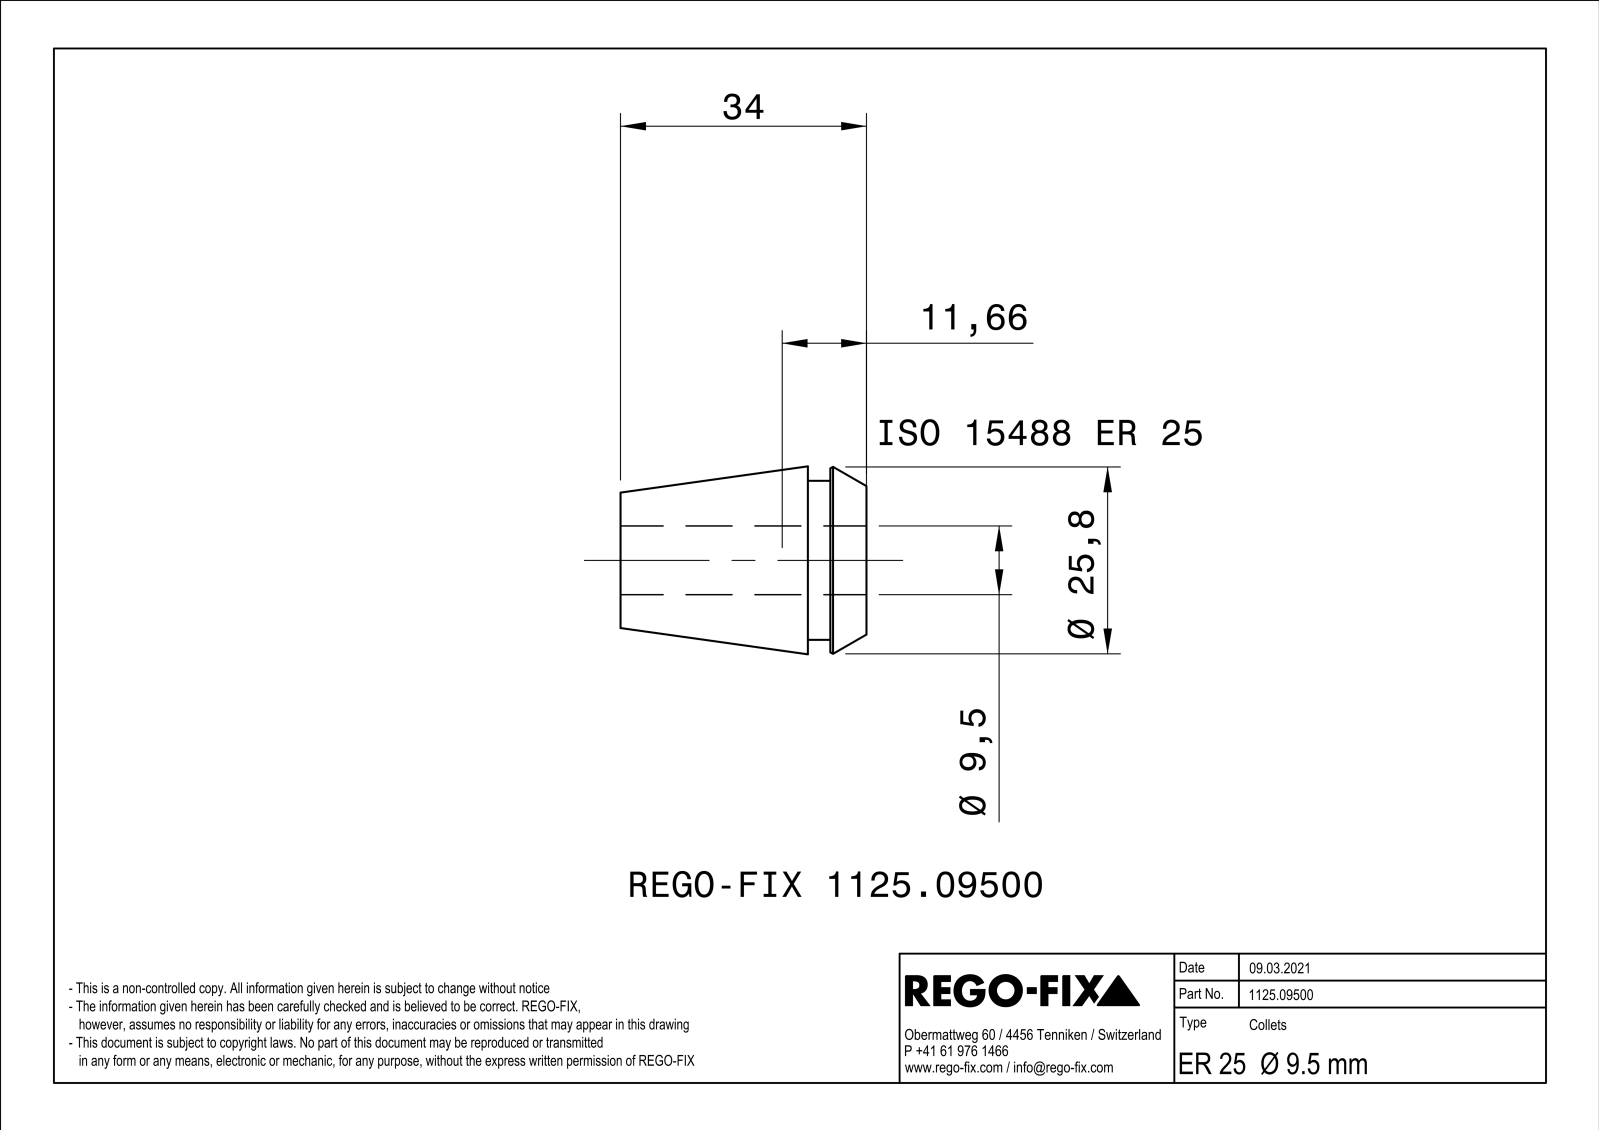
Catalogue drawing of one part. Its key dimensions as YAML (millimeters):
part_name: "NOCUT"
step_written_by: "SIEMENS PLM Software Solid Edge ST10 (AUTOMOTIVE_DESIGN)"
units: millimeters
bodies: {solids: 1, faces: 177, planar: 72, cylindrical: 25, other: 80}
overall_size: [34, 25.99, 25.99]
volume: 8701
surface_area: 9617
round_holes:
  - {diameter: 9.5, count: 1}
round_bosses_or_shafts:
  - {diameter: 22, count: 1}
partial_cylinders:
  - {radius: 0.4, count: 8}
face_to_face_distances: [0.8, 34, 8.1, 25.9, 5, 3.1, 29]
